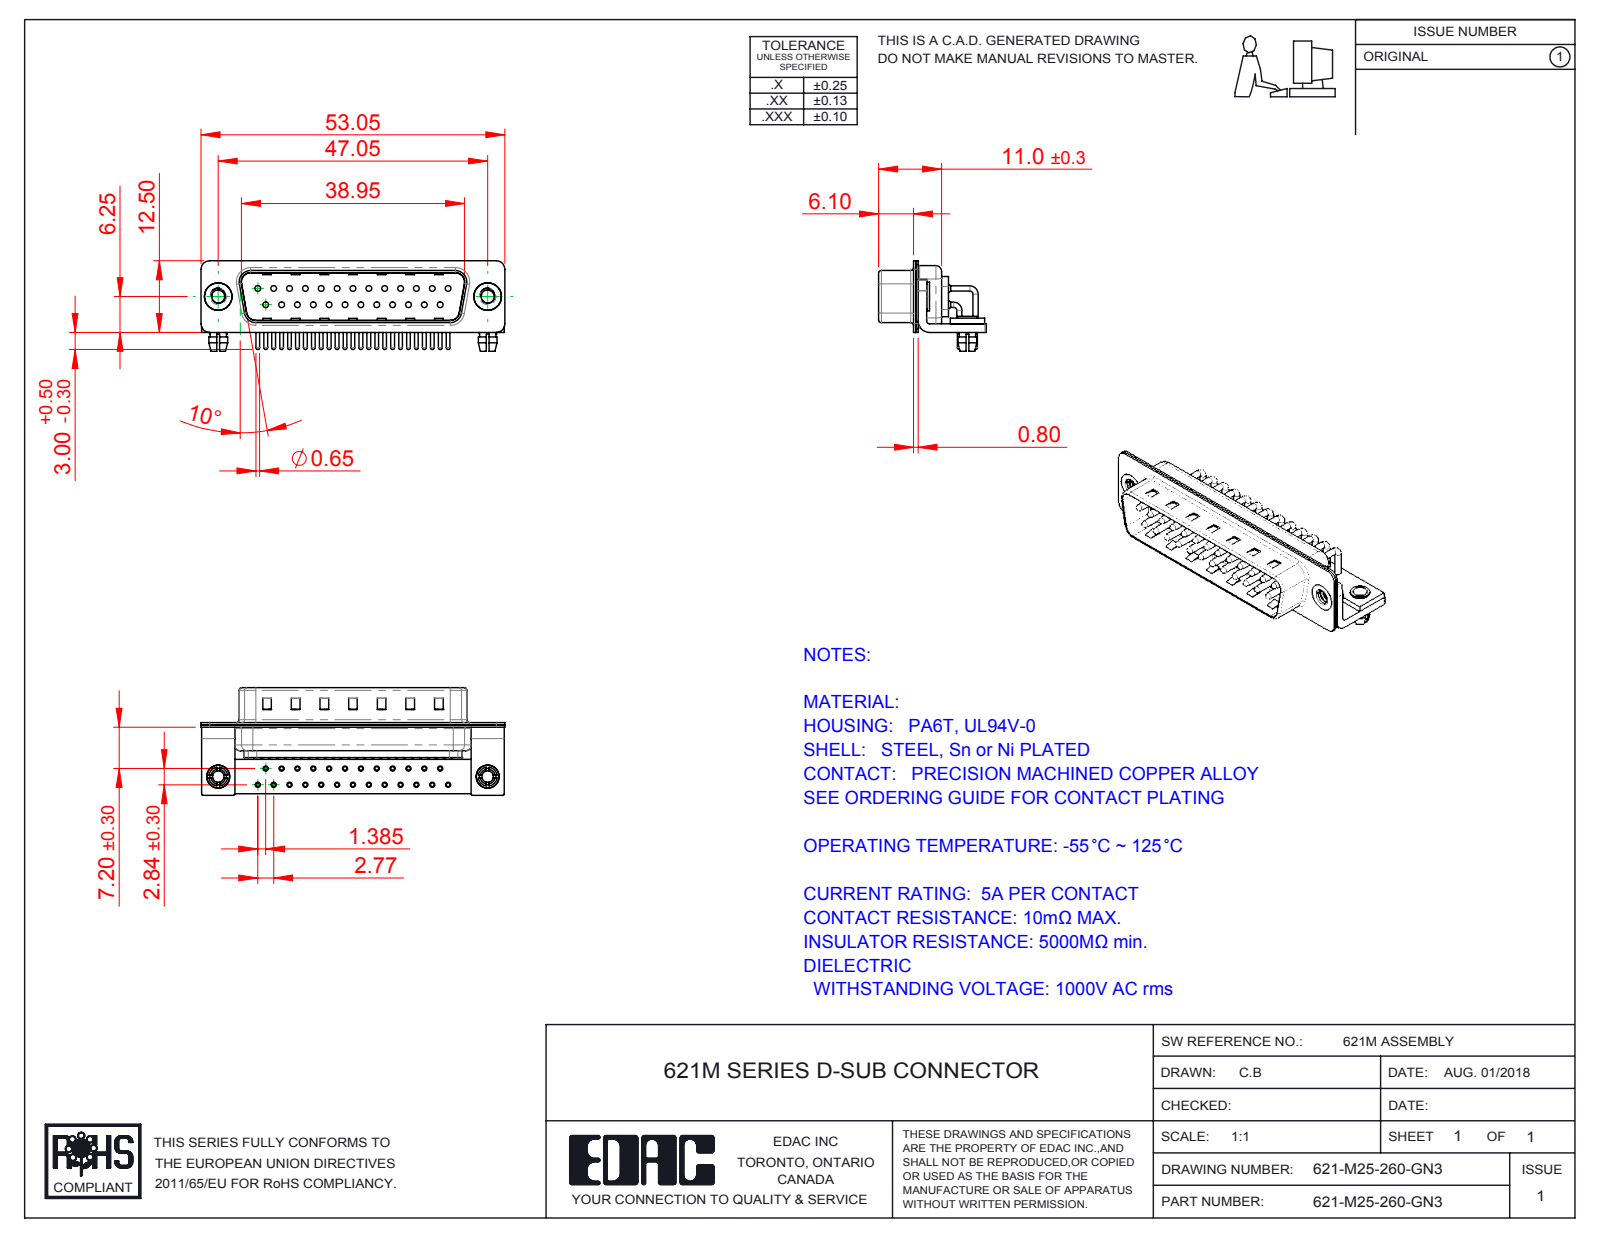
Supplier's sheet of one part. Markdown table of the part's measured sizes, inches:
| quantity | value |
| --- | --- |
| part name | 621M Stabilizer Board_25 Contacts; 621M Shell Rear_25 Contacts; 621M Stabilizer Bracket; 621M 4-40 Threaded Rivet_Stabilizer (+6 more) |
| STEP written by | SolidWorks 2016 (CONFIG_CONTROL_DESIGN) |
| units | inches |
| bodies | 35 solids, 3318 faces (1845 planar, 1141 cylindrical, 332 other) |
| overall size | 2.089 × 0.74 × 0.622 |
| volume | 0.209 in³ |
| surface area | 14.15 in² |
| round holes (diameter × count) | 0.079 × 27, 0.035 × 25, 0.039 × 25, 0.067 × 25, 0.089 × 2, 0.098 × 2, 0.126 × 2, 0.157 × 2, 0.189 × 2 |
| round bosses / shafts (diameter × count) | 0.035 × 33, 0.059 × 25, 0.026 × 25, 0.197 × 2, 0.193 × 2, 0.157 × 2, 0.134 × 2, 0.13 × 2 |
| partial cylindrical surfaces (radius × count) | 0.04 × 25, 0.01 × 16, 0.059 × 16, 0.079 × 13, 0.02 × 9, 0.063 × 8, 0.024 × 4, 0.026 × 4 |
| main face-to-face distances | 0.016, 0.033, 0.049, 0.059, 0.376, 0.409, 0.031, 0.039, 0.327, 0.343 |
| hole center spacings | 0.124, 0.109, 0.327, 0.218, 0.436, 0.545, 0.198, 0.654 |
